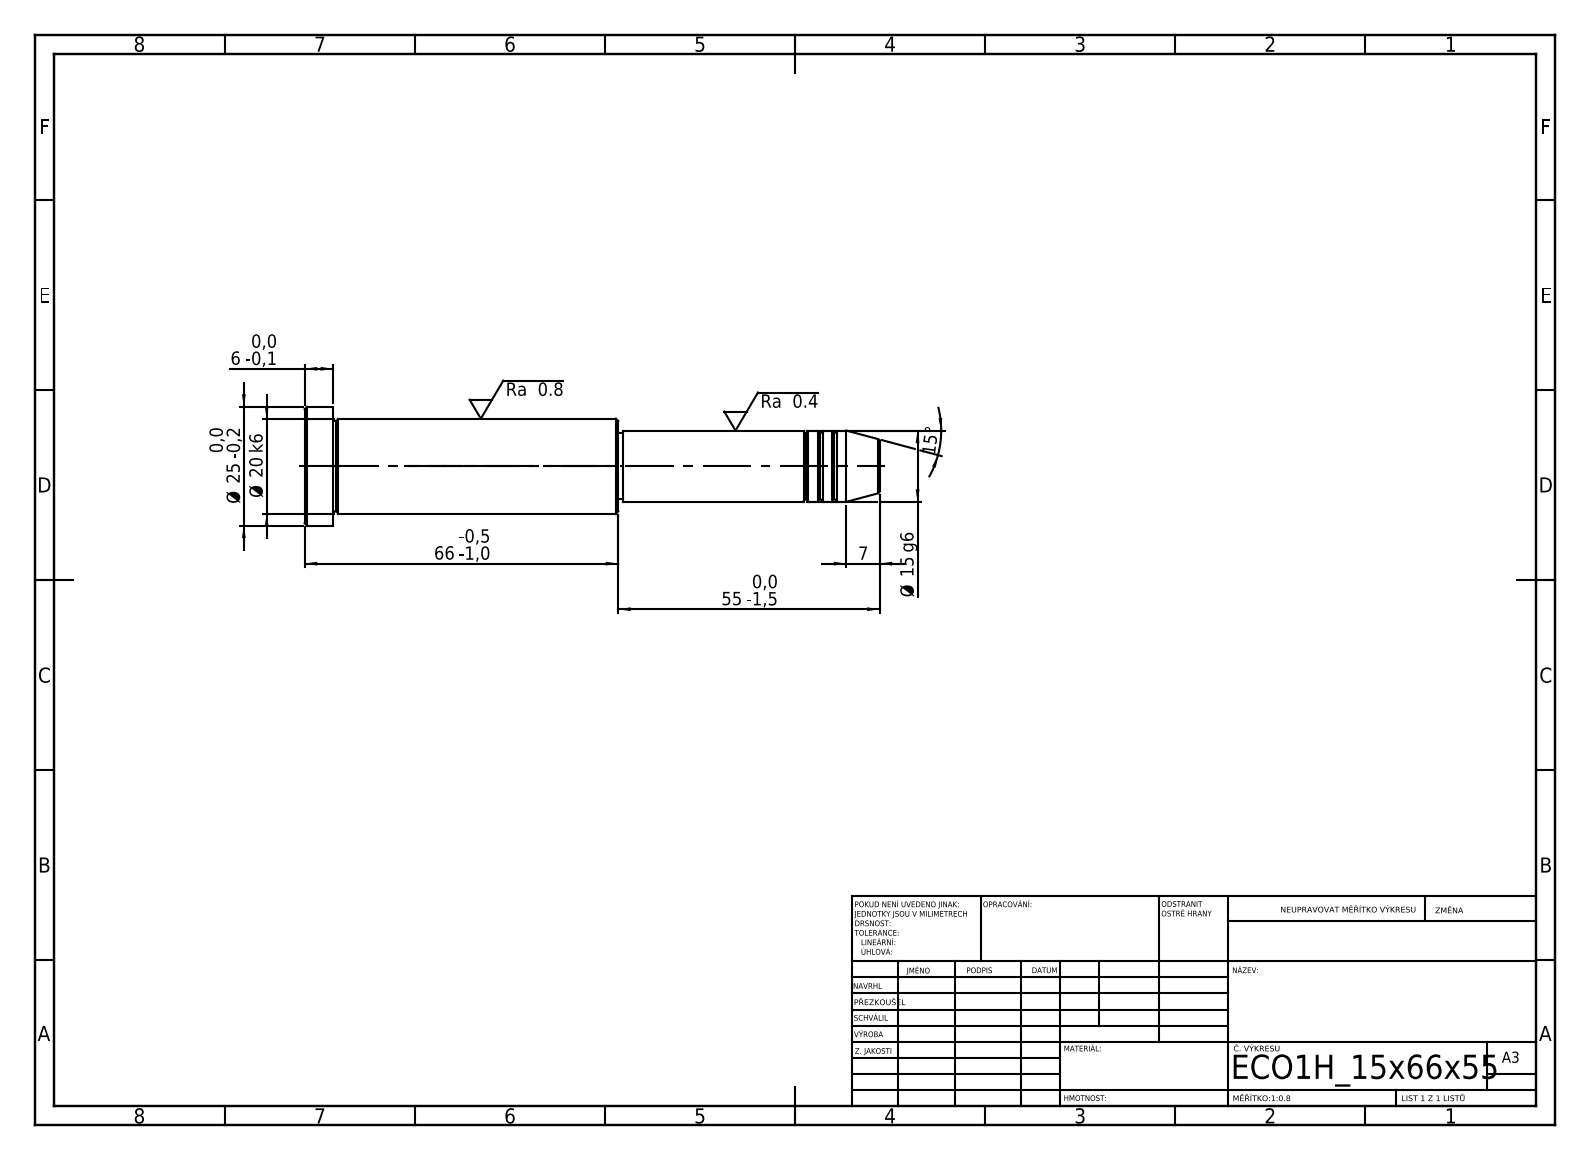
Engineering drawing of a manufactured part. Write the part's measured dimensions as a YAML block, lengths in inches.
step_written_by: "SolidWorks 2019 (CONFIG_CONTROL_DESIGN)"
units: inches
bodies: {solids: 1, faces: 43, planar: 5, cylindrical: 14, other: 24}
overall_size: [4.764, 0.984, 0.984]
volume: 1.899
surface_area: 12.1
round_bosses_or_shafts:
  - {diameter: 0.984, count: 1}
  - {diameter: 0.787, count: 1}
  - {diameter: 0.591, count: 1}
  - {diameter: 0.551, count: 1}
face_to_face_distances: [0.236, 2.362, 2.598, 2.165, 4.528, 4.764, 2.126, 0.039, 2.402, 2.638]
